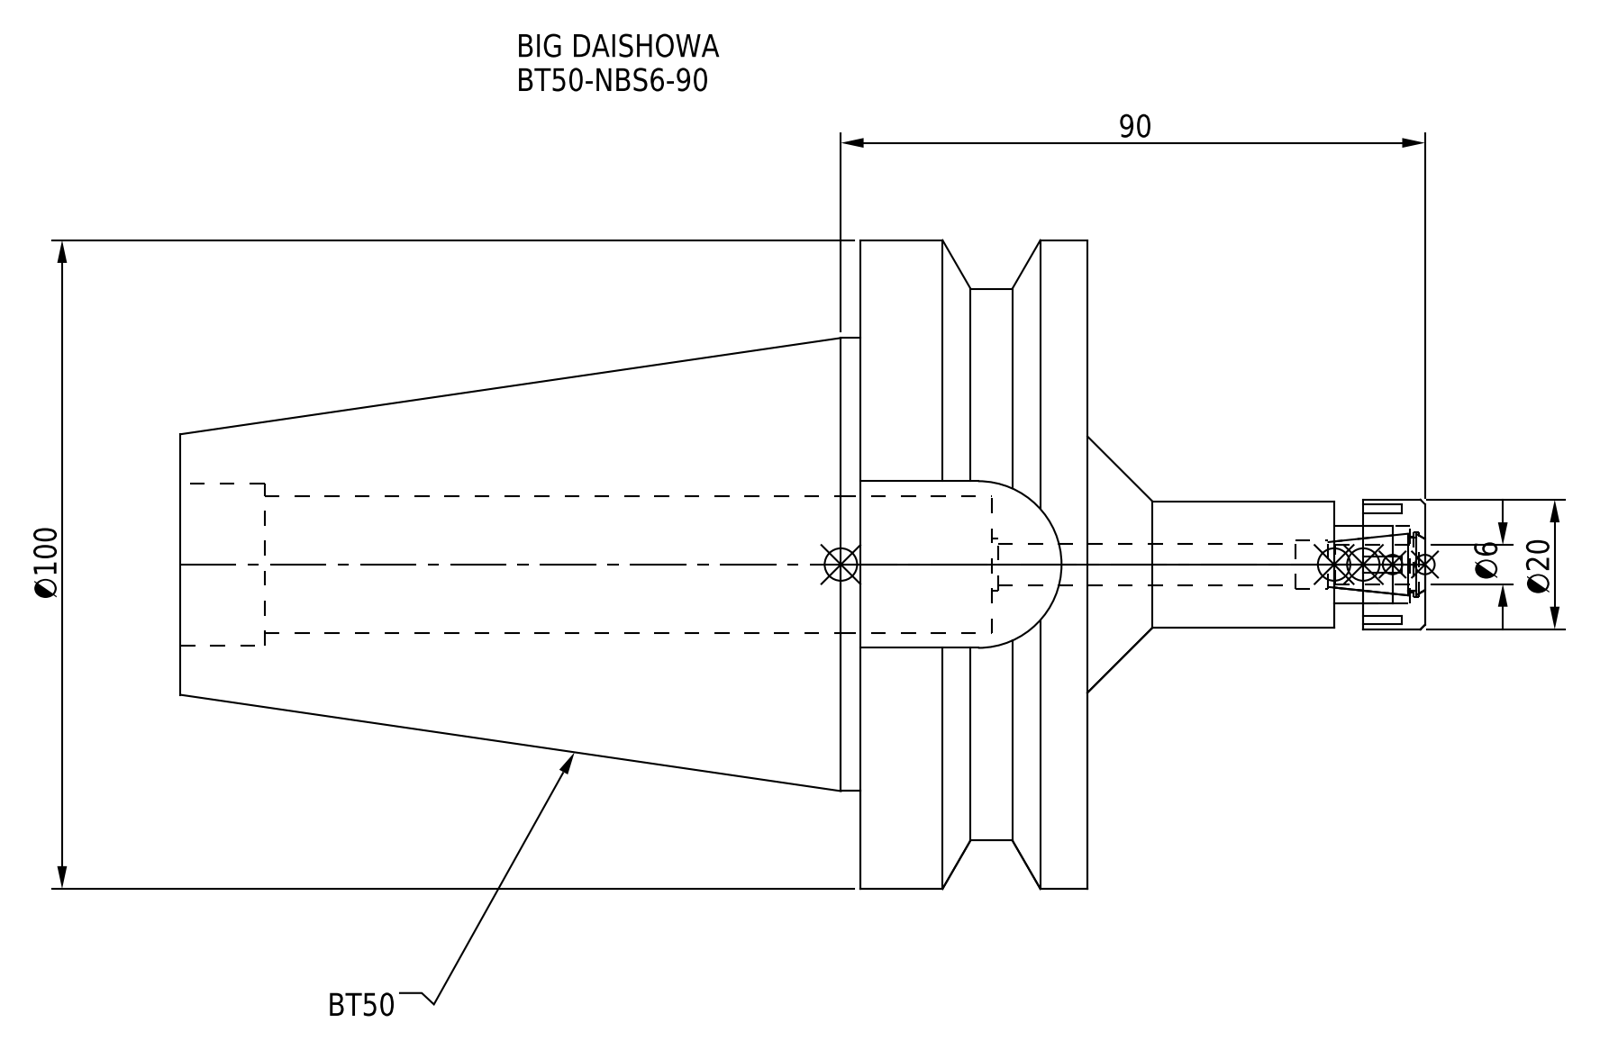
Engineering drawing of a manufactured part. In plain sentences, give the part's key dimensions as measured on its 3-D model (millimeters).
The part is named "BT50-NBS6-90.stp; BT50NB06090-060_ASM.stp; BT50-NBS6-90_1.stp; BT50-NBS6-90-FreeParts (+3 more)". Its 3-D file was written by "SolidWorks 2019 (CONFIG_CONTROL_DESIGN)". It is 2 solids with 93 faces: 45 planar, 34 cylindrical and 14 other. Overall it measures 191.8 by 100 by 100 millimeters. Its volume is 464 223 cubic millimeters and its surface area 58 865 square millimeters. Round holes: 1 of diameter 6.4, 1 of diameter 7.5, 1 of diameter 8, 1 of diameter 8.5, 1 of diameter 10, 1 of diameter 12, 1 of diameter 21.2, 1 of diameter 25. Round bosses or shafts: 1 of diameter 100, 1 of diameter 85, 1 of diameter 69.85, 1 of diameter 20, 1 of diameter 19.5. Partial cylindrical surfaces (rounded edges, fillets, slot ends): 1 of radius 12.85. The main face-to-face distances are 35, 139.8, 104.8, 70.8, 25.7, 14.8, 20.2, 125, 4.5, 52.
